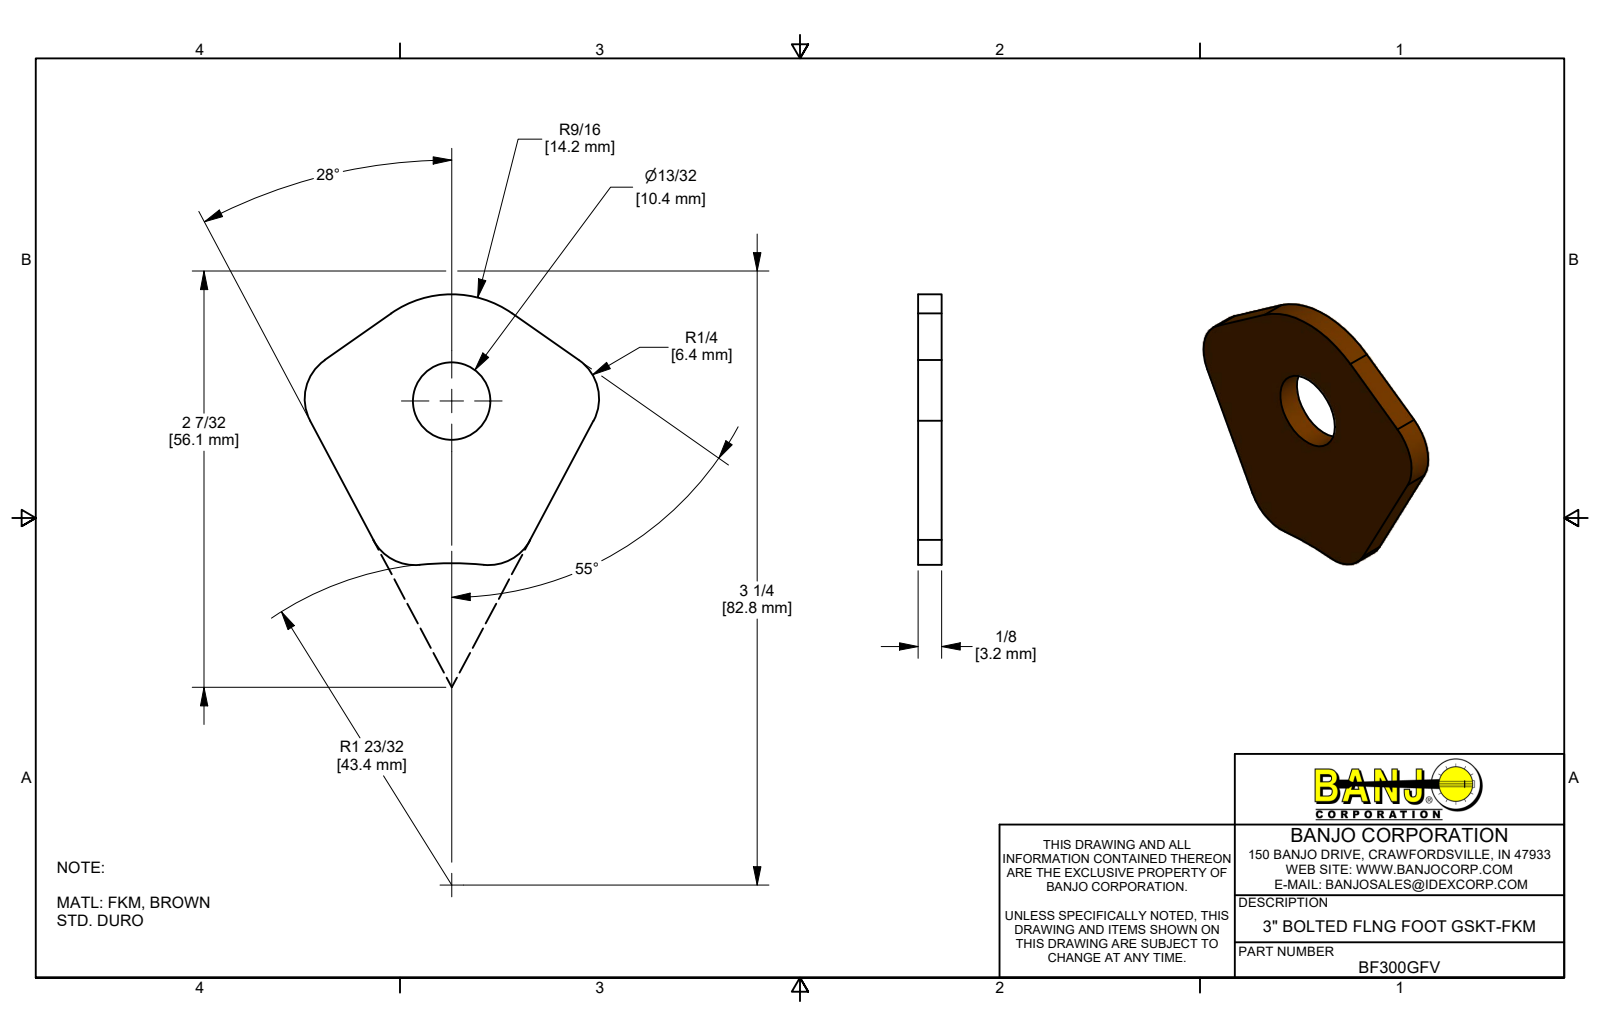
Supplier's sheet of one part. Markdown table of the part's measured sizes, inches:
| quantity | value |
| --- | --- |
| part name | BF300GFV |
| STEP written by | Autodesk Inventor 2019 (AUTOMOTIVE_DESIGN) |
| units | inches |
| bodies | 1 solid, 13 faces (6 planar, 7 cylindrical, 0 other) |
| overall size | 1.563 × 1.436 × 0.125 |
| volume | 0.185 in³ |
| surface area | 3.696 in² |
| round holes (diameter × count) | 0.41 × 1 |
| partial cylindrical surfaces (radius × count) | 0.25 × 4, 0.56 × 1, 1.71 × 1 |
| main face-to-face distances | 0.125 |
